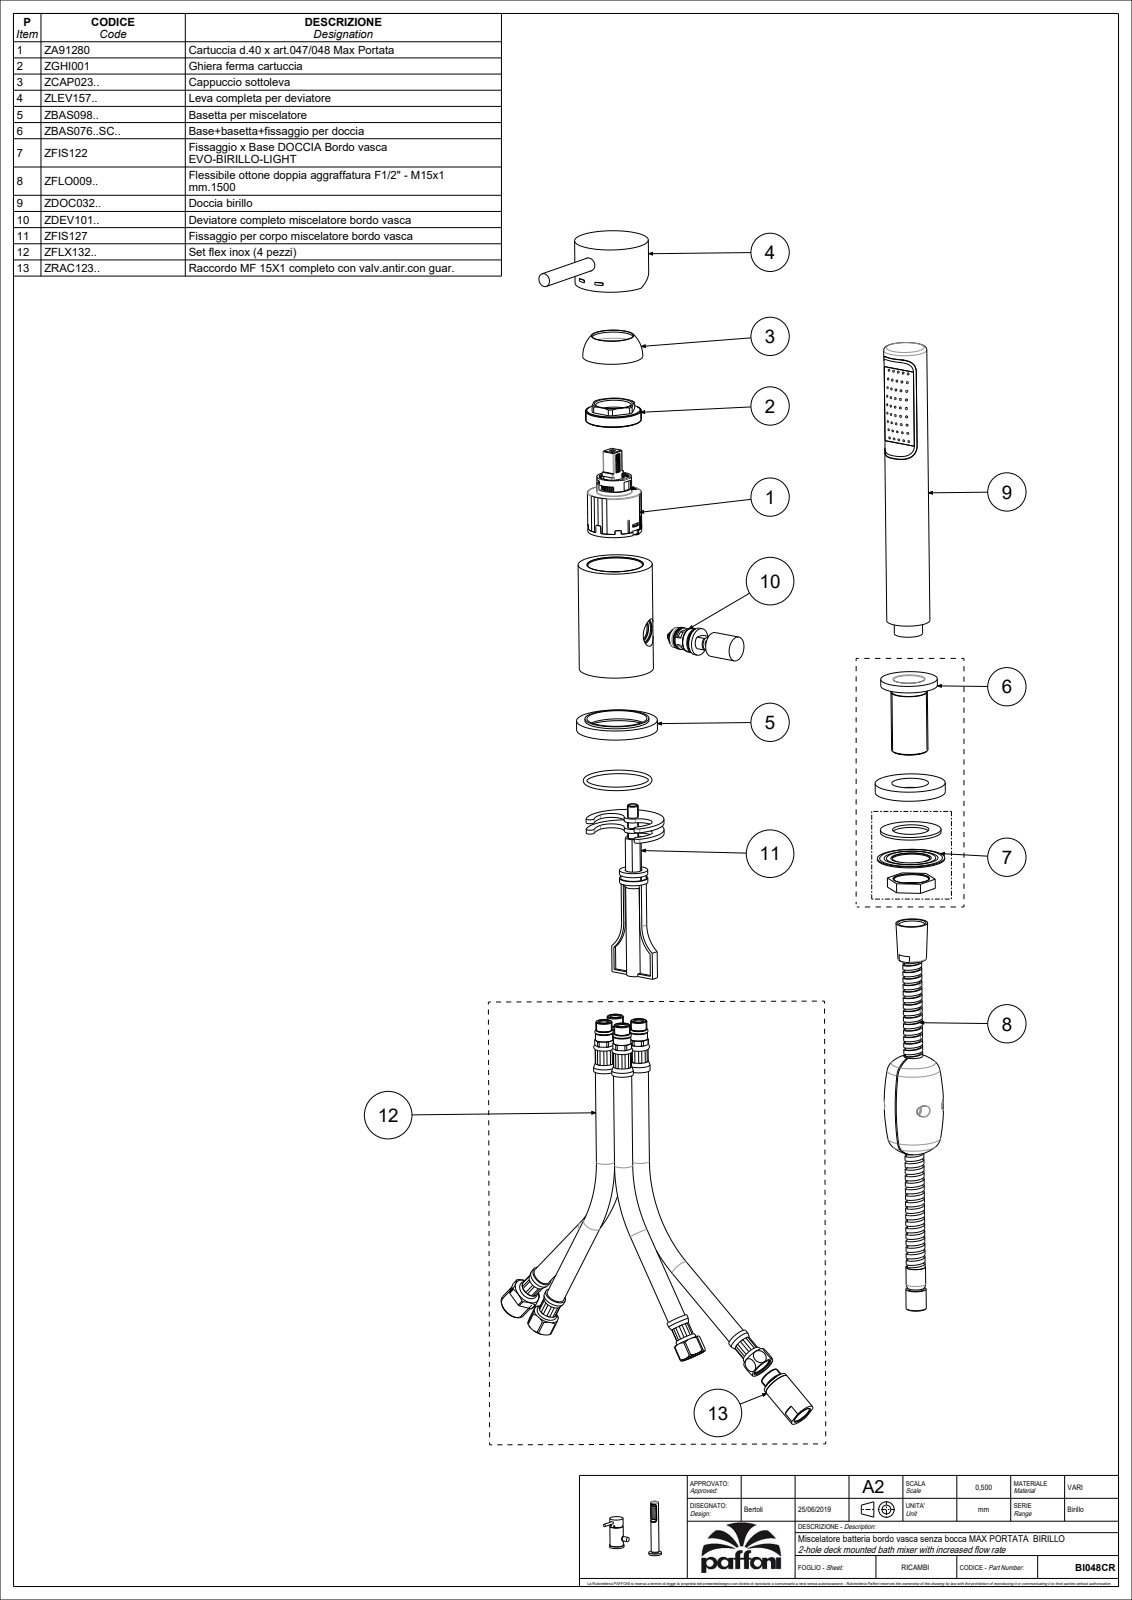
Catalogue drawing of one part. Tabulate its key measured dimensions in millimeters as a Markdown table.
| quantity | value |
| --- | --- |
| part name | BI048CR |
| STEP written by | CREO PARAMETRIC BY PTC INC, 2020044 (CONFIG_CONTROL_DESIGN) |
| units | millimeters |
| bodies | 5 solids, 1633 faces (834 planar, 495 cylindrical, 304 other) |
| overall size | 256 × 222 × 111.85 |
| volume | 285 823 mm³ |
| surface area | 125 108 mm² |
| round holes (diameter × count) | 1.5 × 45, 13 × 4, 7 × 3, 3.3 × 2, 5 × 2, 8 × 2, 10 × 2, 11 × 2, 4 × 1, 4.25 × 1, 8.5 × 1, 9 × 1 |
| round bosses / shafts (diameter × count) | 12.8 × 4, 20 × 2, 5 × 2, 60 × 1, 55 × 1, 54.7 × 1, 52 × 1, 47.5 × 1 |
| partial cylindrical surfaces (radius × count) | 0.5 × 21, 0.15 × 12, 0.2 × 12, 1.5 × 11, 1.1 × 10, 0.25 × 9, 2 × 8, 0.3 × 6 |
| main face-to-face distances | 2, 7, 5, 10, 114.8, 107.8, 9, 220, 213, 59.3 |
| hole center spacings | 7.91, 13.76, 20.01, 6.5, 13, 26.39, 4.5, 19.5 |
